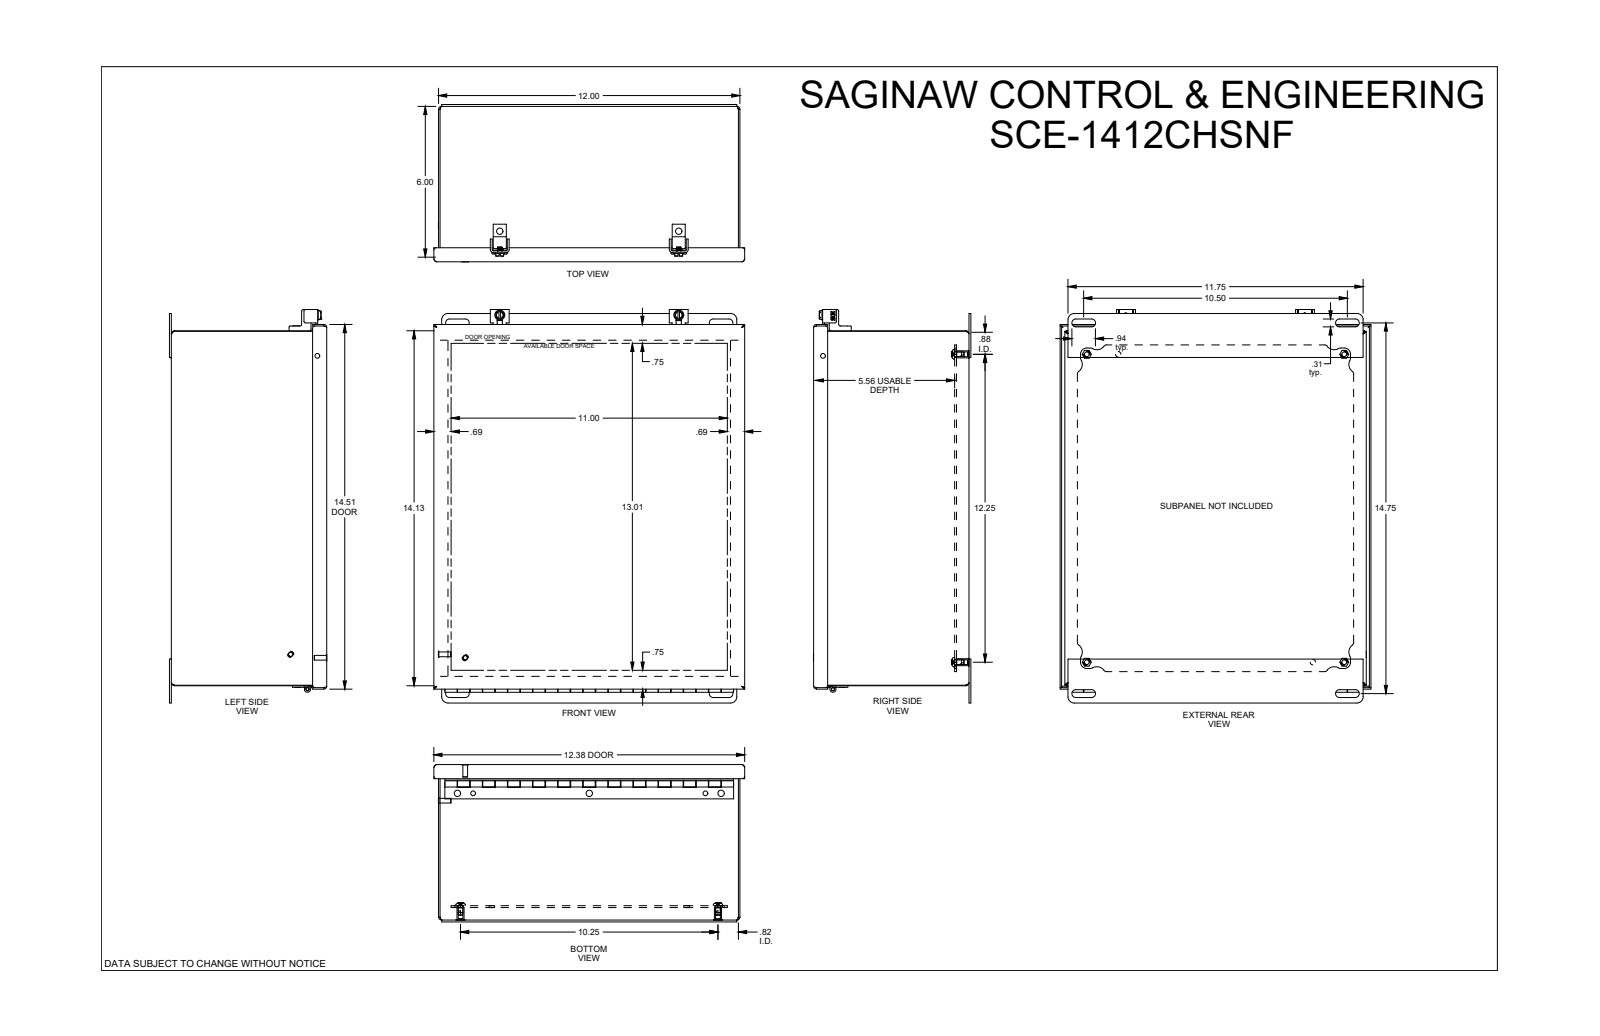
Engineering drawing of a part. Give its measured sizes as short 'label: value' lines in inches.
name: SCE-1412CHNF
written by: SolidWorks 2019 (AUTOMOTIVE_DESIGN)
unit: in
bodies: 33 solids, 1058 faces (530 planar, 325 cylindrical, 203 other)
size: 15.5 × 13.104 × 6.265
volume: 60.8 in³; area: 1 898 in²
holes: 8× ⌀0.193, 4× ⌀0.19, 4× ⌀0.25, 4× ⌀0.281, 2× ⌀0.156, 2× ⌀0.218, 2× ⌀0.266, 1× ⌀0.126, 1× ⌀0.187
bosses: 12× ⌀0.188, 8× ⌀0.256, 4× ⌀0.373, 4× ⌀0.28, 2× ⌀0.396, 2× ⌀0.188, 1× ⌀0.246, 1× ⌀0.123
rounds: 46× R0.01, 33× R0.06, 16× R0.25, 8× R0.05, 8× R0.125, 8× R0.156, 8× R0.344, 6× R0.027
face distances: 0.06, 6.125, 6.185, 6.065, 11.94, 0.075, 0.51, 0.435, 0.57, 5.555
hole spacings: 15.972, 12.249, 1.065, 1.25, 2.166, 2.48, 3.542, 4.167
